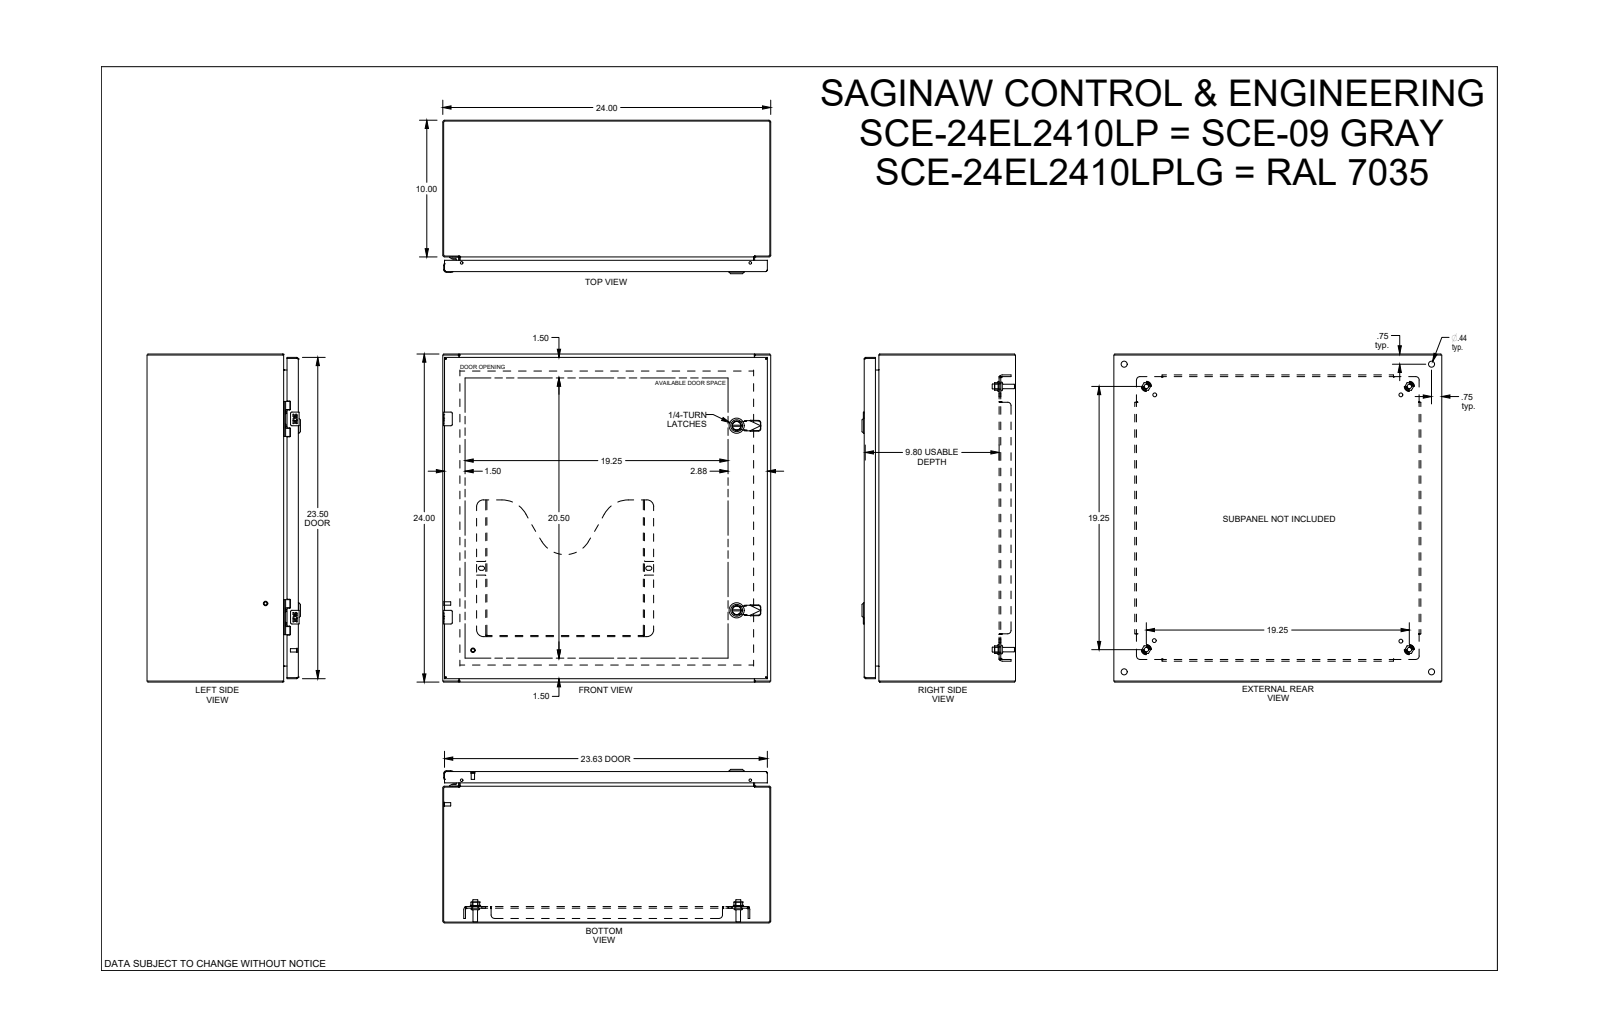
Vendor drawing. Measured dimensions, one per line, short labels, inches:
name: SCE-24EL2410LP
written by: SolidWorks 2021 (AUTOMOTIVE_DESIGN)
unit: in
bodies: 45 solids, 2819 faces (1099 planar, 850 cylindrical, 870 other)
size: 24 × 24 × 11.23
volume: 254.2 in³; area: 6 154 in²
holes: 4× ⌀0.172, 4× ⌀0.205, 4× ⌀0.244, 4× ⌀0.266, 4× ⌀0.281, 4× ⌀0.367, 4× ⌀0.375, 4× ⌀0.437, 4× ⌀0.5, 2× ⌀0.04, 2× ⌀0.188, 2× ⌀0.197
bosses: 6× ⌀0.17, 4× ⌀0.366, 4× ⌀0.332, 4× ⌀0.25, 4× ⌀0.248, 4× ⌀0.24, 3× ⌀0.196, 2× ⌀1.102
rounds: 56× R0.012, 28× R0.01, 24× R0.015, 20× R0.02, 17× R0.04, 13× R0.06, 12× R0.029, 12× R0.1
face distances: 0.075, 23.925, 0.06, 11.073, 10.998, 11.013, 10.938, 1.2, 9.873, 23.85
hole spacings: 20.938, 18.641, 0.985, 14.5, 20.38, 0.875, 19.25, 0.02
